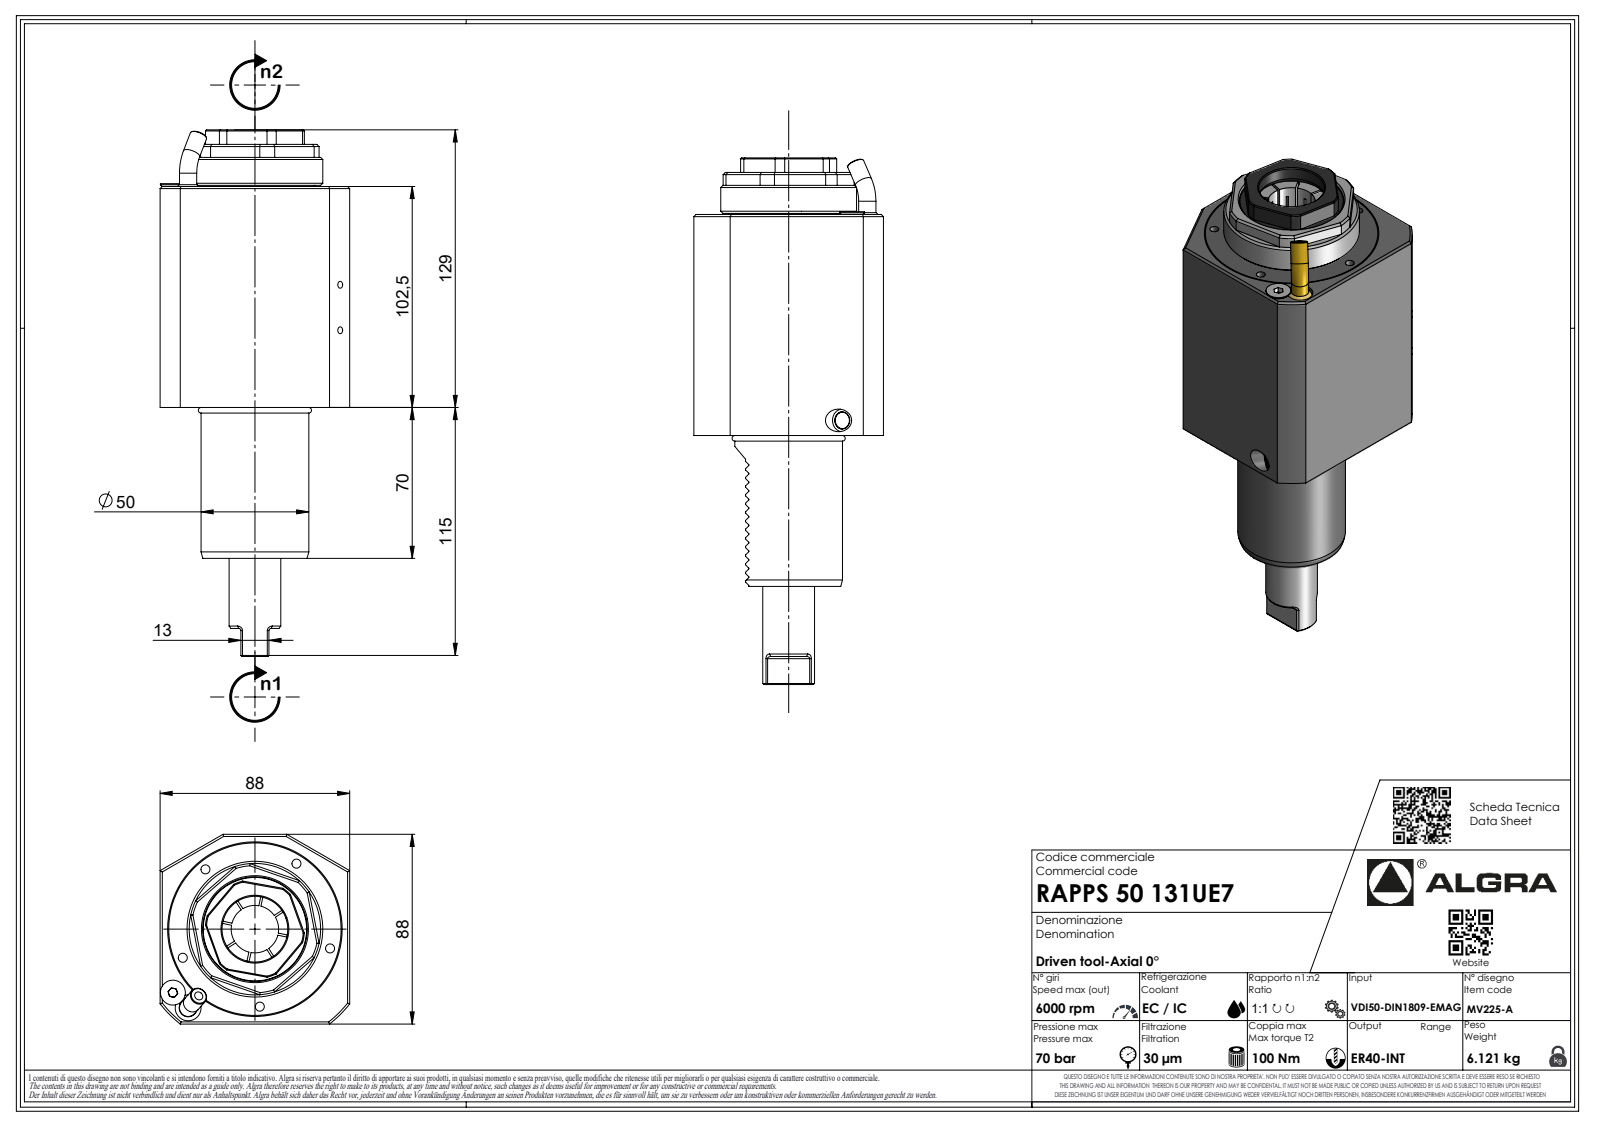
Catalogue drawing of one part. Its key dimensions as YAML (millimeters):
part_name: "RAPPS50131UE7"
step_written_by: "SolidWorks 2023 (AUTOMOTIVE_DESIGN)"
units: millimeters
bodies: {solids: 1, faces: 458, planar: 291, cylindrical: 64, other: 103}
overall_size: [244.25, 88, 88]
volume: 952024
surface_area: 67873
round_holes:
  - {diameter: 2.1, count: 1}
round_bosses_or_shafts:
  - {diameter: 8, count: 2}
  - {diameter: 63, count: 1}
  - {diameter: 55, count: 1}
  - {diameter: 50, count: 1}
  - {diameter: 49.2, count: 1}
  - {diameter: 24, count: 1}
  - {diameter: 6.37, count: 1}
  - {diameter: 1.7, count: 1}
partial_cylinders:
  - {radius: 0.3, count: 15}
  - {radius: 0.33, count: 7}
  - {radius: 0.52, count: 7}
  - {radius: 3.7, count: 7}
  - {radius: 1, count: 2}
  - {radius: 0.21, count: 1}
  - {radius: 23, count: 1}
  - {radius: 30.5, count: 1}
face_to_face_distances: [88, 102.5, 2.83, 26.25, 128.75, 14.14, 198.75, 172.5, 70, 11.31]
